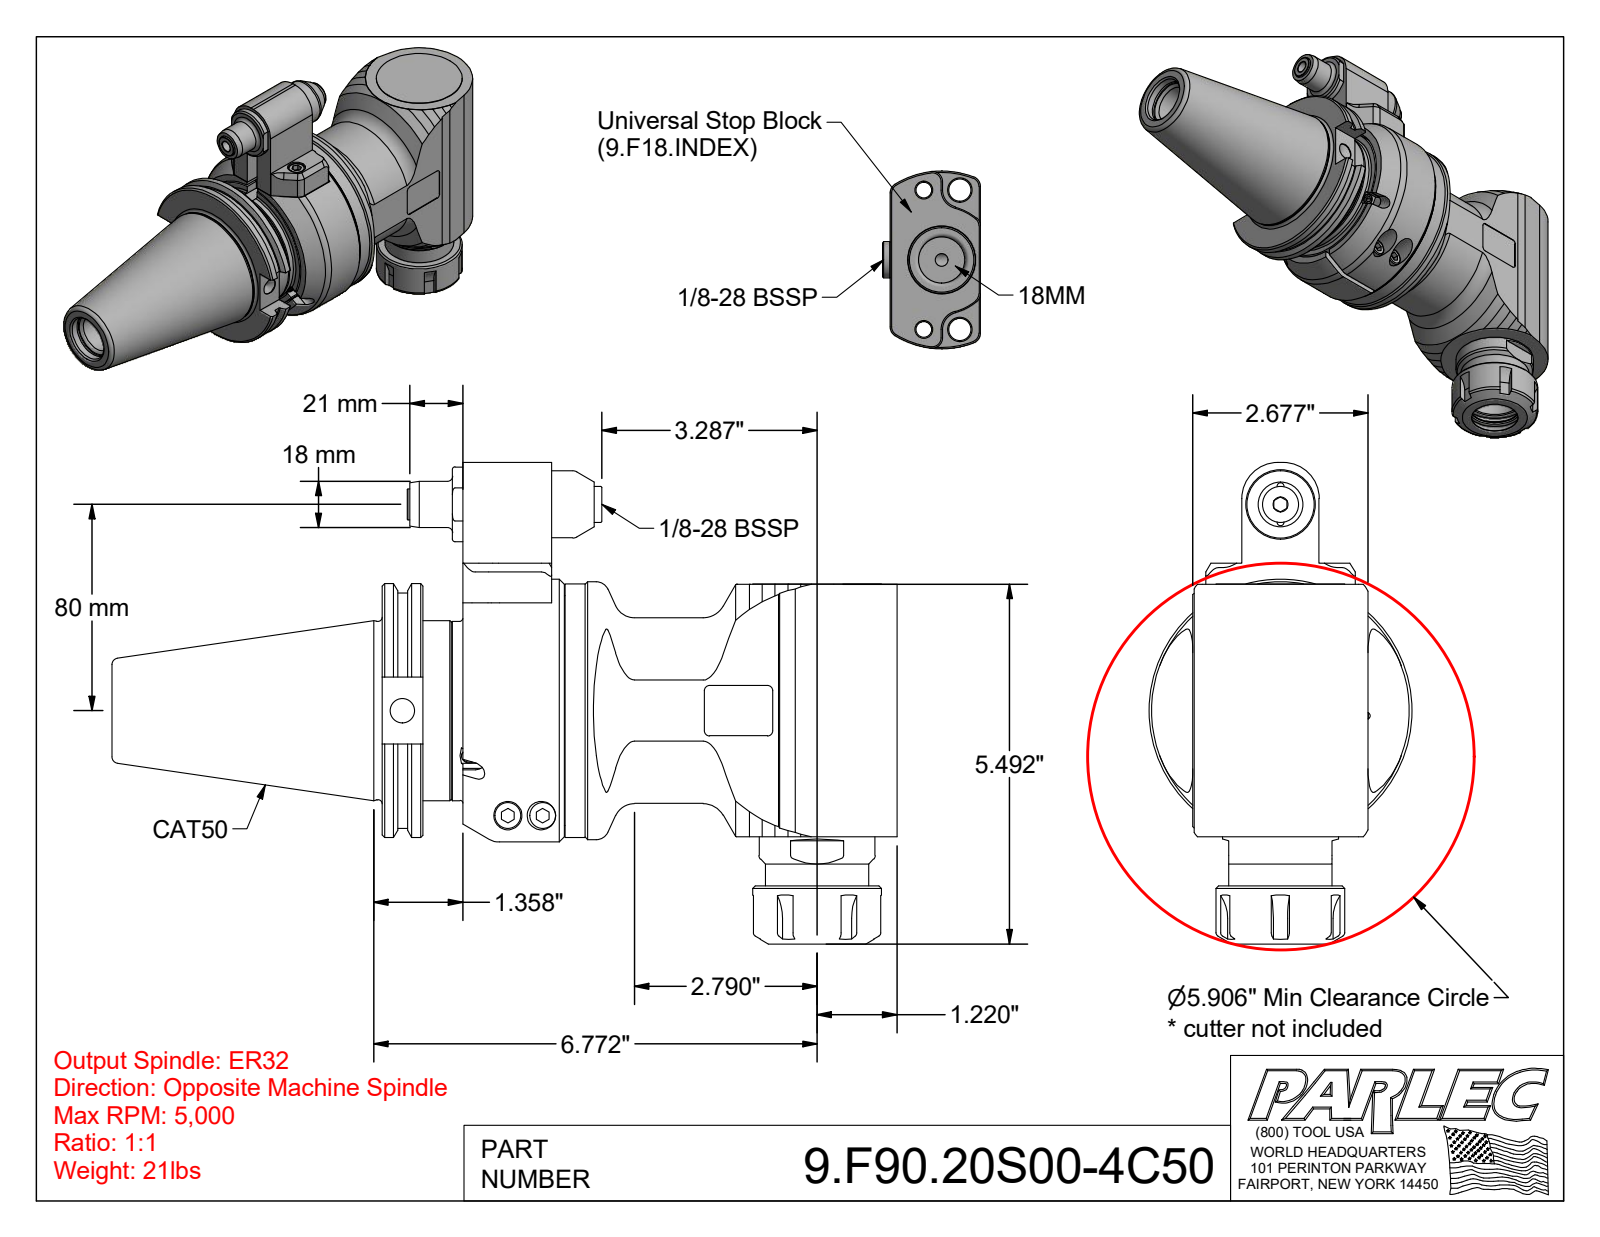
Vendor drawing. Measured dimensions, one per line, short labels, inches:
name: 9.F90.20S00-4C50; 9_F90_20S00; 9_GA1_458_2 (Type 1, Cat50, 80mm)
written by: Autodesk Inventor 2020 (AUTOMOTIVE_DESIGN)
unit: in
bodies: 8 solids, 528 faces (249 planar, 115 cylindrical, 164 other)
size: 11.992 × 7.352 × 4.016
volume: 90.59 in³; area: 287.9 in²
holes: 2× ⌀0.102, 2× ⌀0.197, 2× ⌀0.409, 2× ⌀0.433, 2× ⌀0.492, 2× ⌀1.063, 1× ⌀0.098, 1× ⌀0.118, 1× ⌀0.256, 1× ⌀0.276, 1× ⌀0.375, 1× ⌀0.472
bosses: 6× ⌀0.236, 4× ⌀0.394, 2× ⌀0.709, 2× ⌀0.098, 1× ⌀4.016, 1× ⌀3.937, 1× ⌀3.875, 1× ⌀3.874
rounds: 12× R0.079, 6× R0.591, 4× R0.157, 2× R0.02, 2× R0.039, 2× R0.138, 2× R0.197, 2× R0.551
face distances: 1.26, 0.748, 0.285, 0.904, 2.163, 0.197, 0.625, 1.529, 2.789, 1.555
hole spacings: 0.276, 0.512, 0.551, 1.72, 2.272, 2.659, 2.874, 3.15
